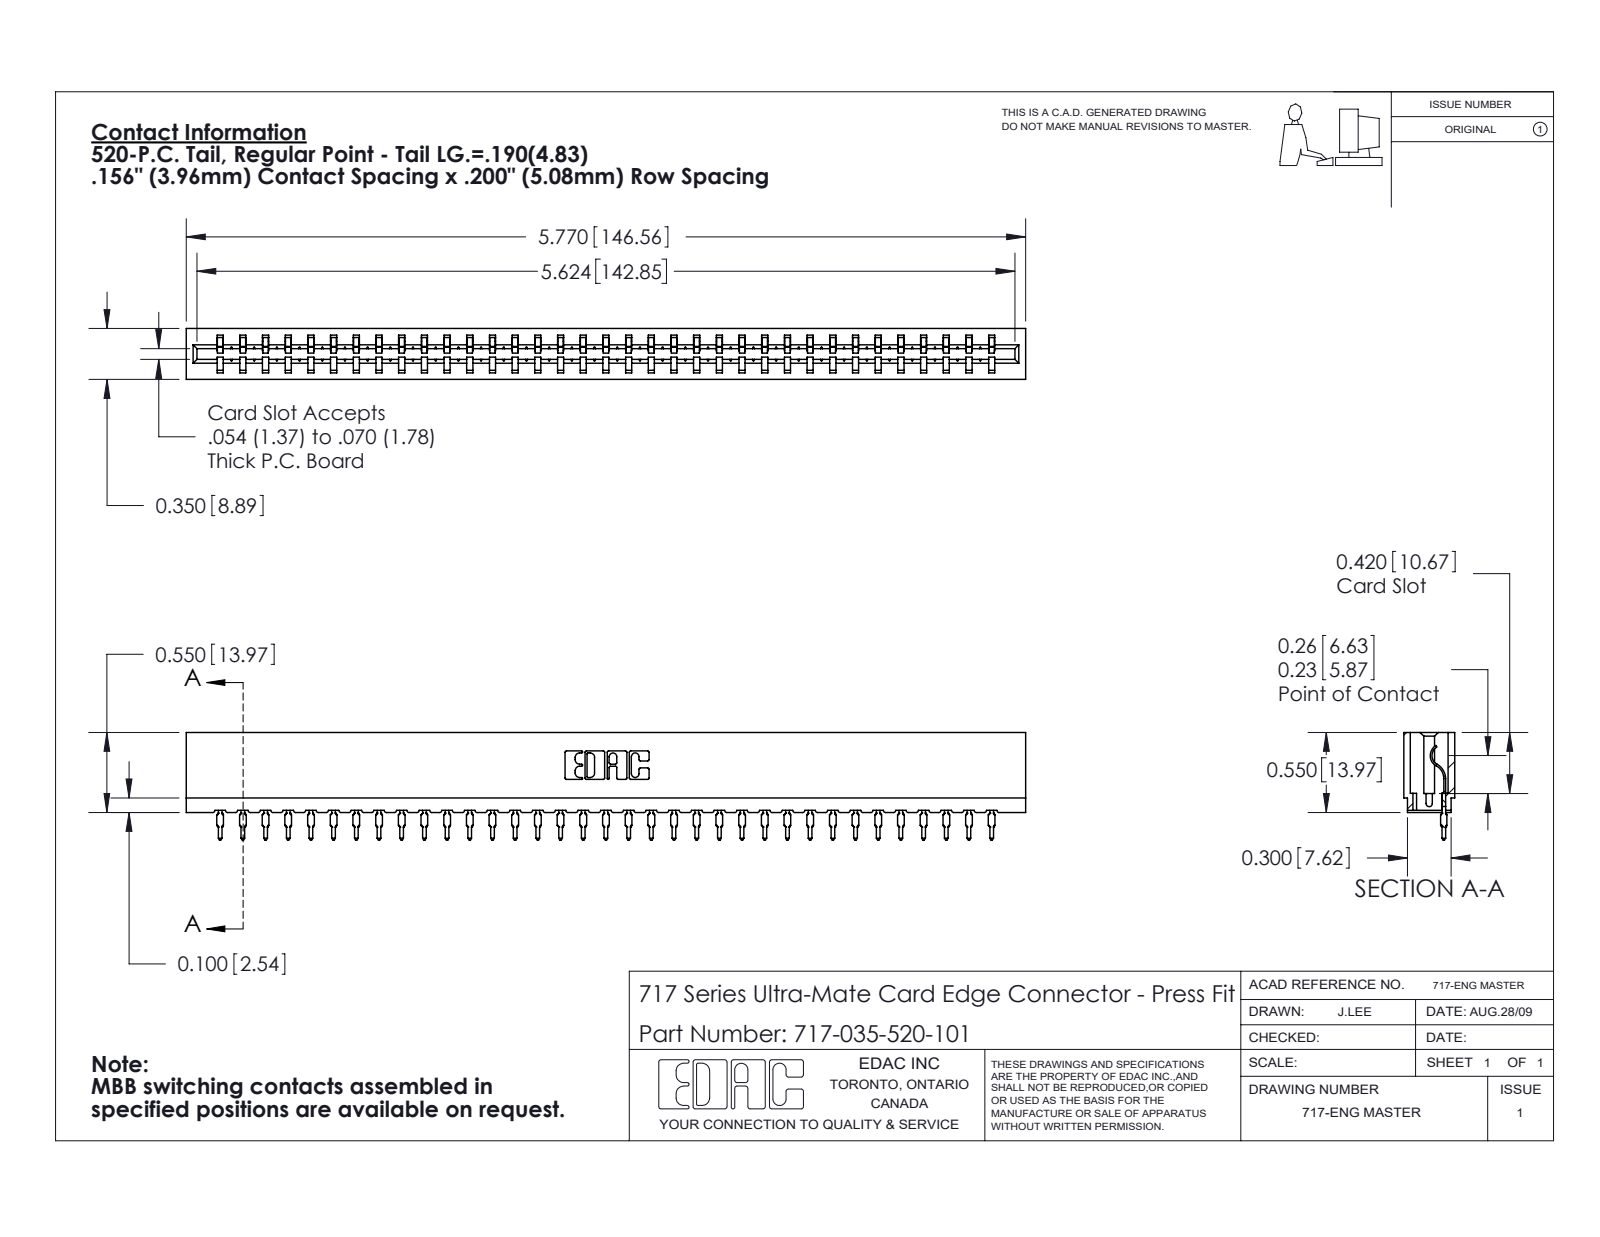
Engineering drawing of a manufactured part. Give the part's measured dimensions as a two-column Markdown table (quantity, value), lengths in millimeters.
| quantity | value |
| --- | --- |
| part name | 717 Part_Insulator Option - 06; 717-035-520-101; 745-292-001_520 |
| STEP written by | SolidWorks 2020 (CONFIG_CONTROL_DESIGN) |
| units | millimeters |
| bodies | 36 solids, 4049 faces (2434 planar, 705 cylindrical, 910 other) |
| overall size | 146.6 × 18.8 × 8.9 |
| volume | 12 400 mm³ |
| surface area | 17 030 mm² |
| partial cylindrical surfaces (radius × count) | 0.4 × 70, 0.5 × 70, 0.3 × 22, 0.2 × 6, 0.8 × 6, 0.1 × 4, 0.3 × 4, 0.7 × 3 |
| main face-to-face distances | 5.4, 3.5, 8.9, 1.9, 1.1, 7.7, 2.4, 4.2, 0.6, 4 |
